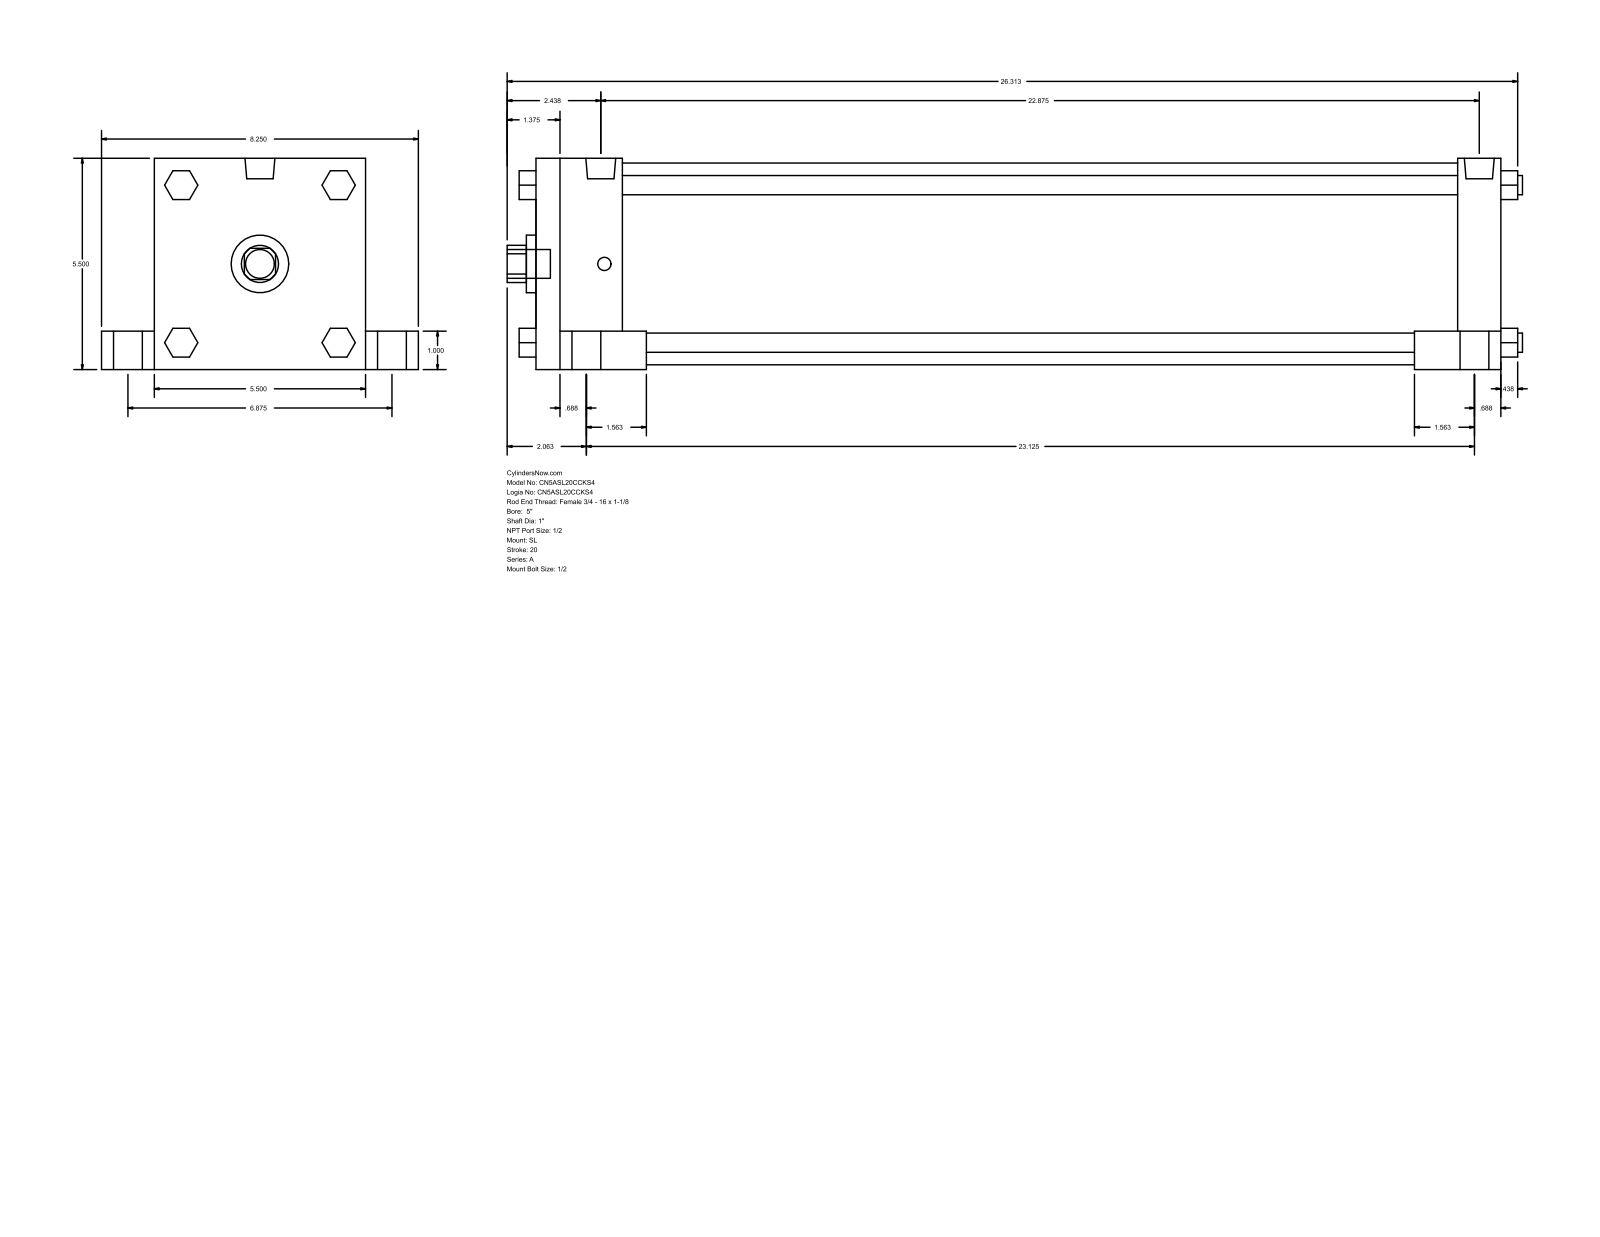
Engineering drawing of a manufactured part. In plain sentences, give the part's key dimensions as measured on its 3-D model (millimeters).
The part is named "A_SL__0500_1". Its 3-D file was written by "GSSL Pune (CONFIG_CONTROL_DESIGN)". It is 0 solids with 150 faces: 114 planar, 36 cylindrical and 0 other. Overall it measures 671.51 by 209.55 by 139.7 millimeters. Round holes: 1 of diameter 25.4, 1 of diameter 38.1, 1 of diameter 133.35. Round bosses or shafts: 5 of diameter 19.05, 4 of diameter 25.4, 4 of diameter 12.7, 4 of diameter 8.73, 2 of diameter 19.77. Partial cylindrical surfaces (rounded edges, fillets, slot ends): 1 of radius 12.29. The main face-to-face distances are 139.7, 638.18, 57.15, 581.03, 25.4, 114.3, 34.93, 174.63, 609.6, 552.45.
